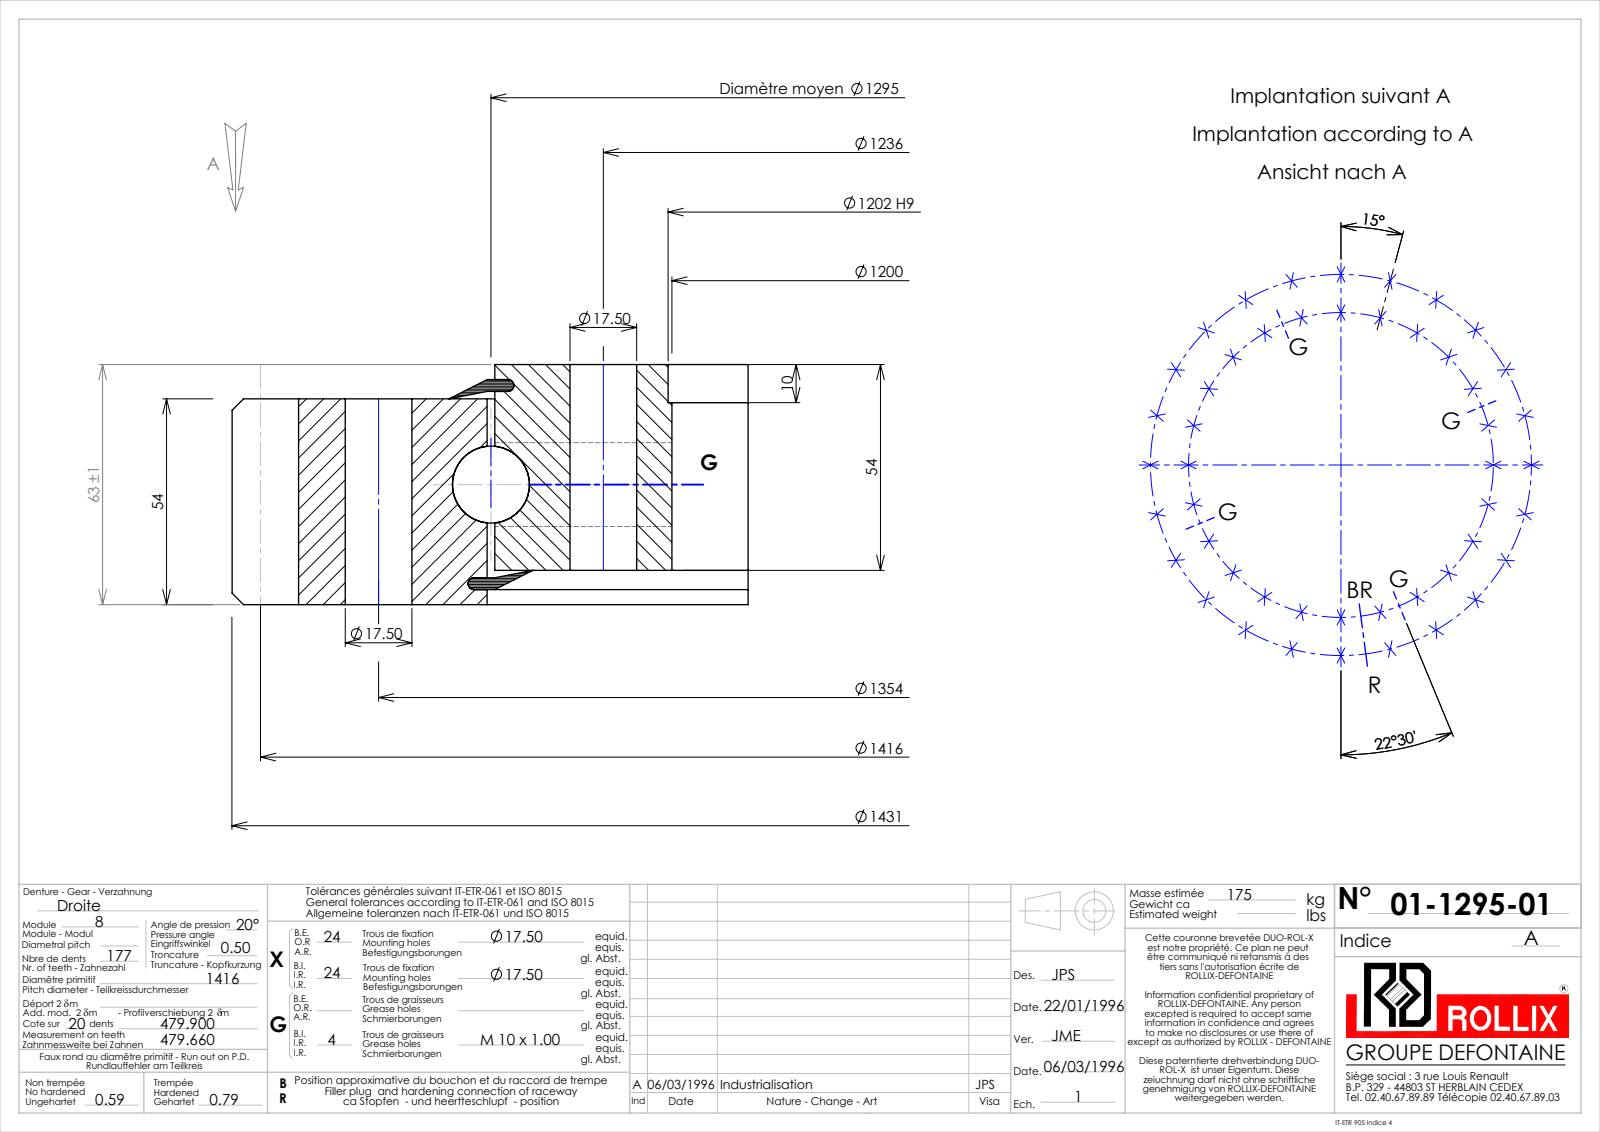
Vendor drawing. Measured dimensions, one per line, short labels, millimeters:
name: 01-1295-01
written by: SolidWorks 2016 (CONFIG_CONTROL_DESIGN)
unit: mm
bodies: 5 solids, 1225 faces (367 planar, 475 cylindrical, 383 other)
size: 1430.99 × 1430.94 × 63
volume: 21 730 000 mm³; area: 2 554 000 mm²
holes: 48× ⌀17.5, 4× ⌀9, 1× ⌀1200, 1× ⌀1202, 1× ⌀1297.03
bosses: 1× ⌀1292.98
rounds: 1× R698, 1× R715.5
face distances: 54, 9, 45, 63, 7.05, 55.95, 1.95, 46.95, 3.95, 59.05
hole spacings: 677, 176.73, 350.44, 518.15, 824.26, 957.42, 1074.2, 1172.6
